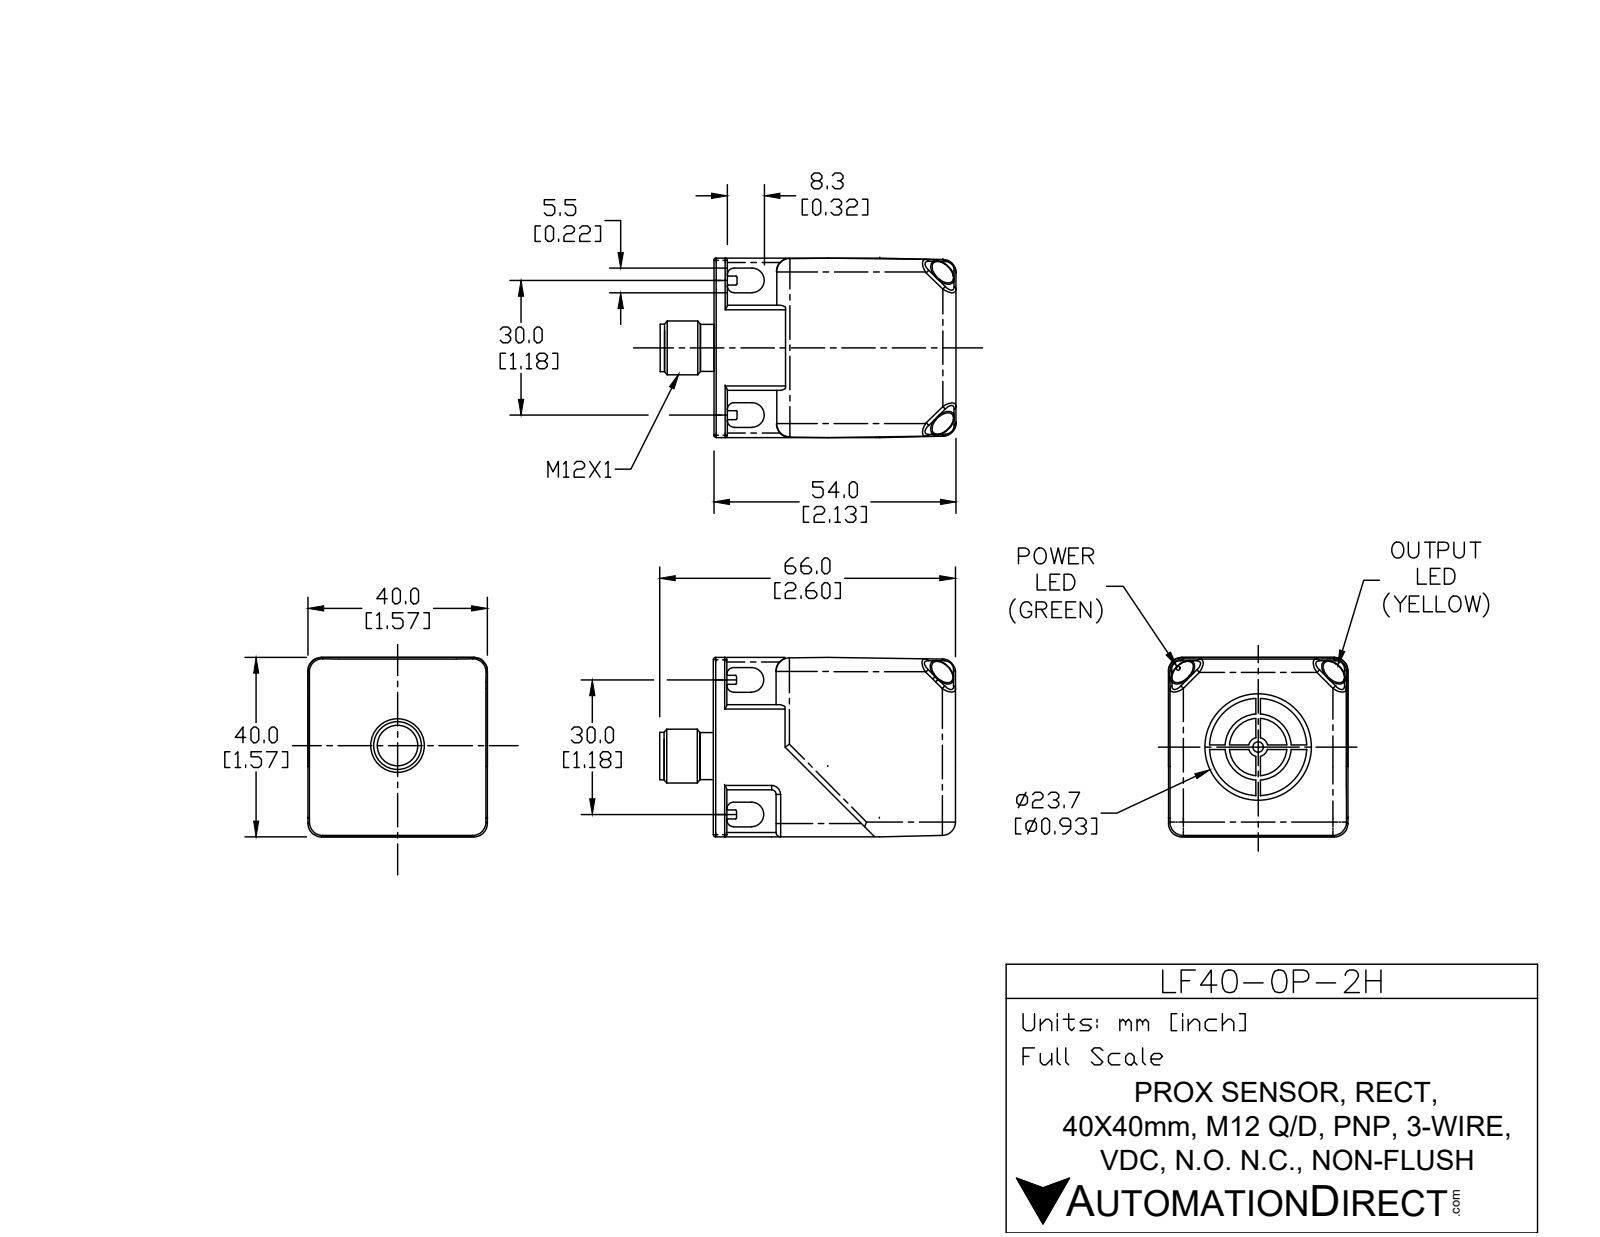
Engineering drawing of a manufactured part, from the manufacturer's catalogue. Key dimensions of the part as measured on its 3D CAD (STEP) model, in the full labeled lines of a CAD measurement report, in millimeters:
Part name (STEP PRODUCT): LF40-0P-2H
STEP written by: SolidWorks 2017 (AUTOMOTIVE_DESIGN)
Units: millimetres
Bodies: 1 solid, 222 faces (110 planar, 99 cylindrical, 13 other)
Overall size (bounding box): 66 × 40 × 40
Volume: 78 080 mm³ · Surface area: 15 060 mm²
Round holes (diameter × count): ⌀8.4 ×1, ⌀9.2 ×1, ⌀14.8 ×1, ⌀23.7 ×1
Round bosses / shafts (diameter × count): ⌀21.7 ×1, ⌀12.8 ×1, ⌀12 ×1, ⌀10.6 ×1, ⌀10.5 ×1, ⌀9 ×1, ⌀7 ×1, ⌀2.3 ×1
Partial cylindrical surfaces — rounded edges, fillets, slot ends (radius × count): R0.2 ×16, R1 ×10, R3 ×10, R1.5 ×8, R0.5 ×4, R2.7 ×4, R5 ×4, R0.6 ×1
Main face-to-face distances: 40, 54, 10.5, 29.5, 30, 3, 51, 8.3, 2.3, 7.7
Hole centre spacings: 2
